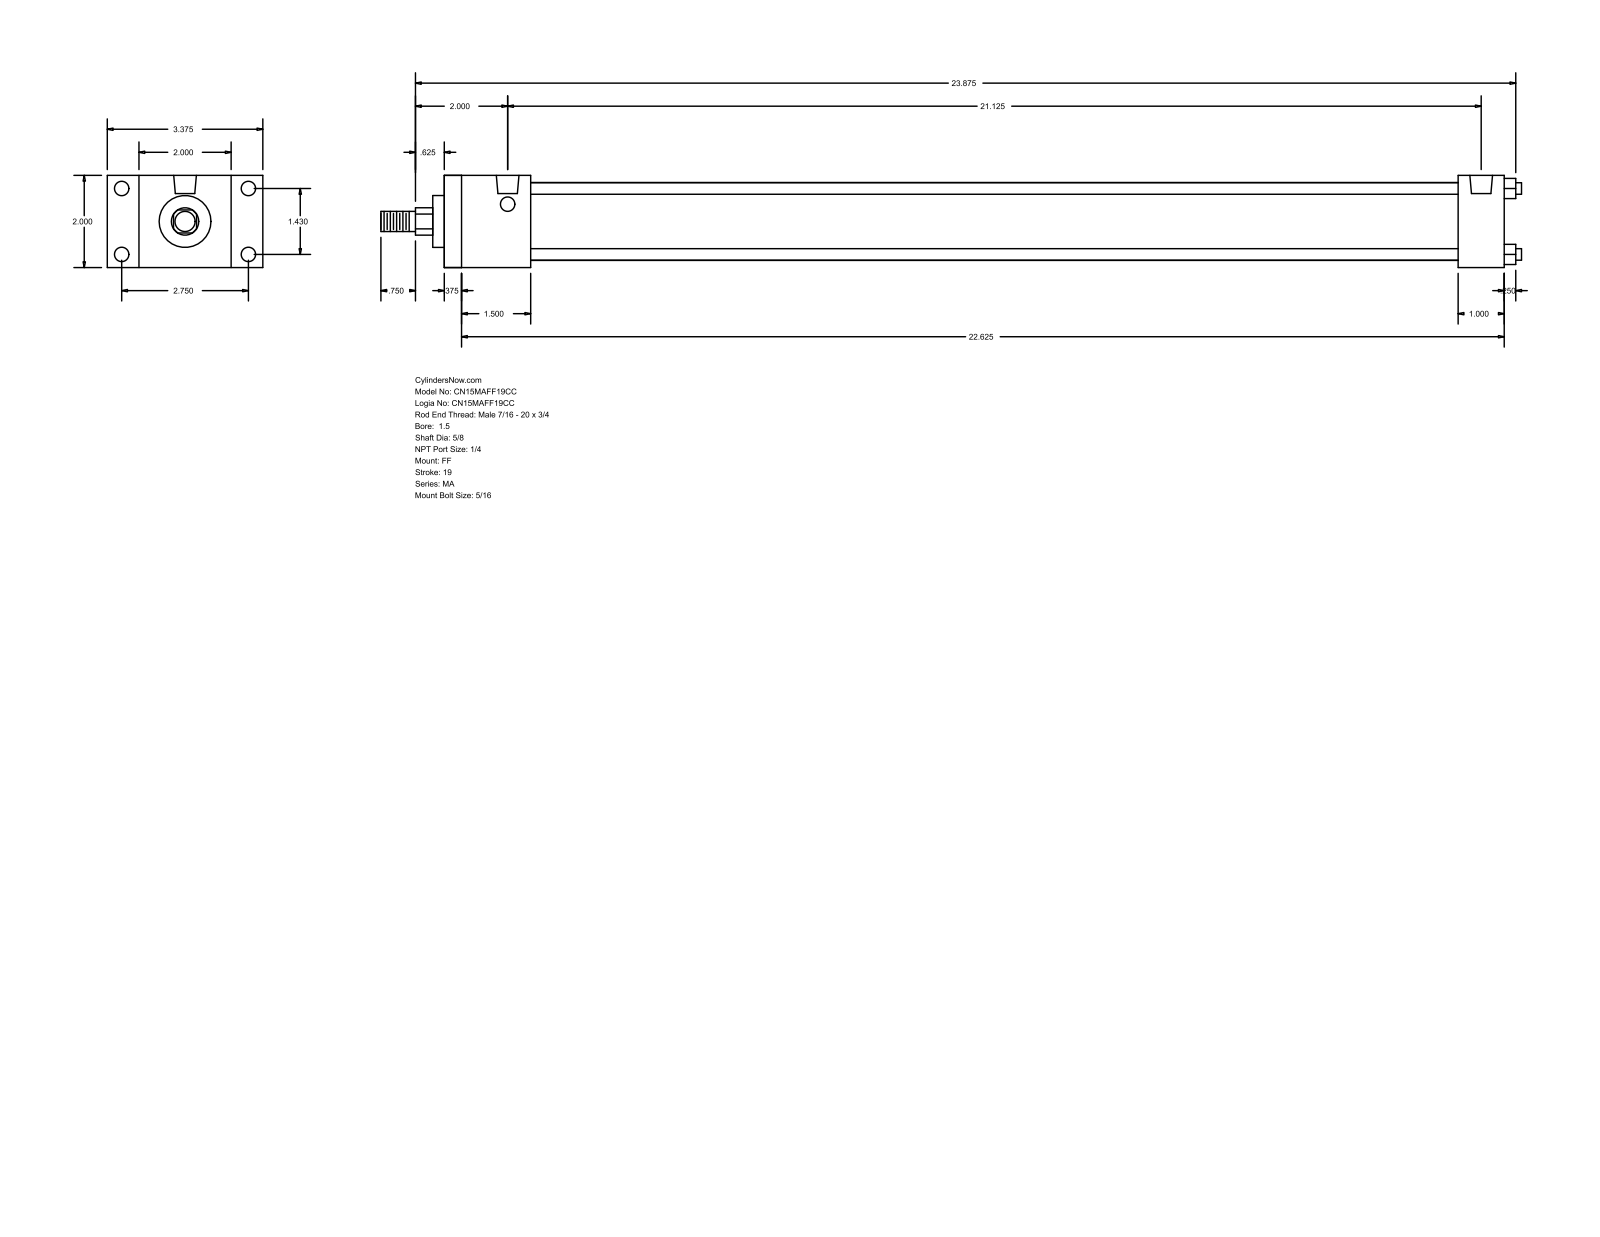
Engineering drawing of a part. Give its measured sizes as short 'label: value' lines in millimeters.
name: MA_FF__0150_0.625
written by: GSSL Pune (CONFIG_CONTROL_DESIGN)
unit: mm
bodies: 0 solids, 92 faces (64 planar, 28 cylindrical, 0 other)
size: 628.65 × 85.72 × 50.8
holes: 8× ⌀7.94, 2× ⌀12.49
bosses: 4× ⌀6.35, 1× ⌀42.93, 1× ⌀28.57, 1× ⌀15.88, 1× ⌀11.11
rounds: 1× R7.54
face distances: 50.8, 584.2, 9.52, 574.68, 47.62, 558.79, 38.1, 549.27, 511.17, 536.58
hole spacings: 36.32, 69.84, 78.72, 536.58
